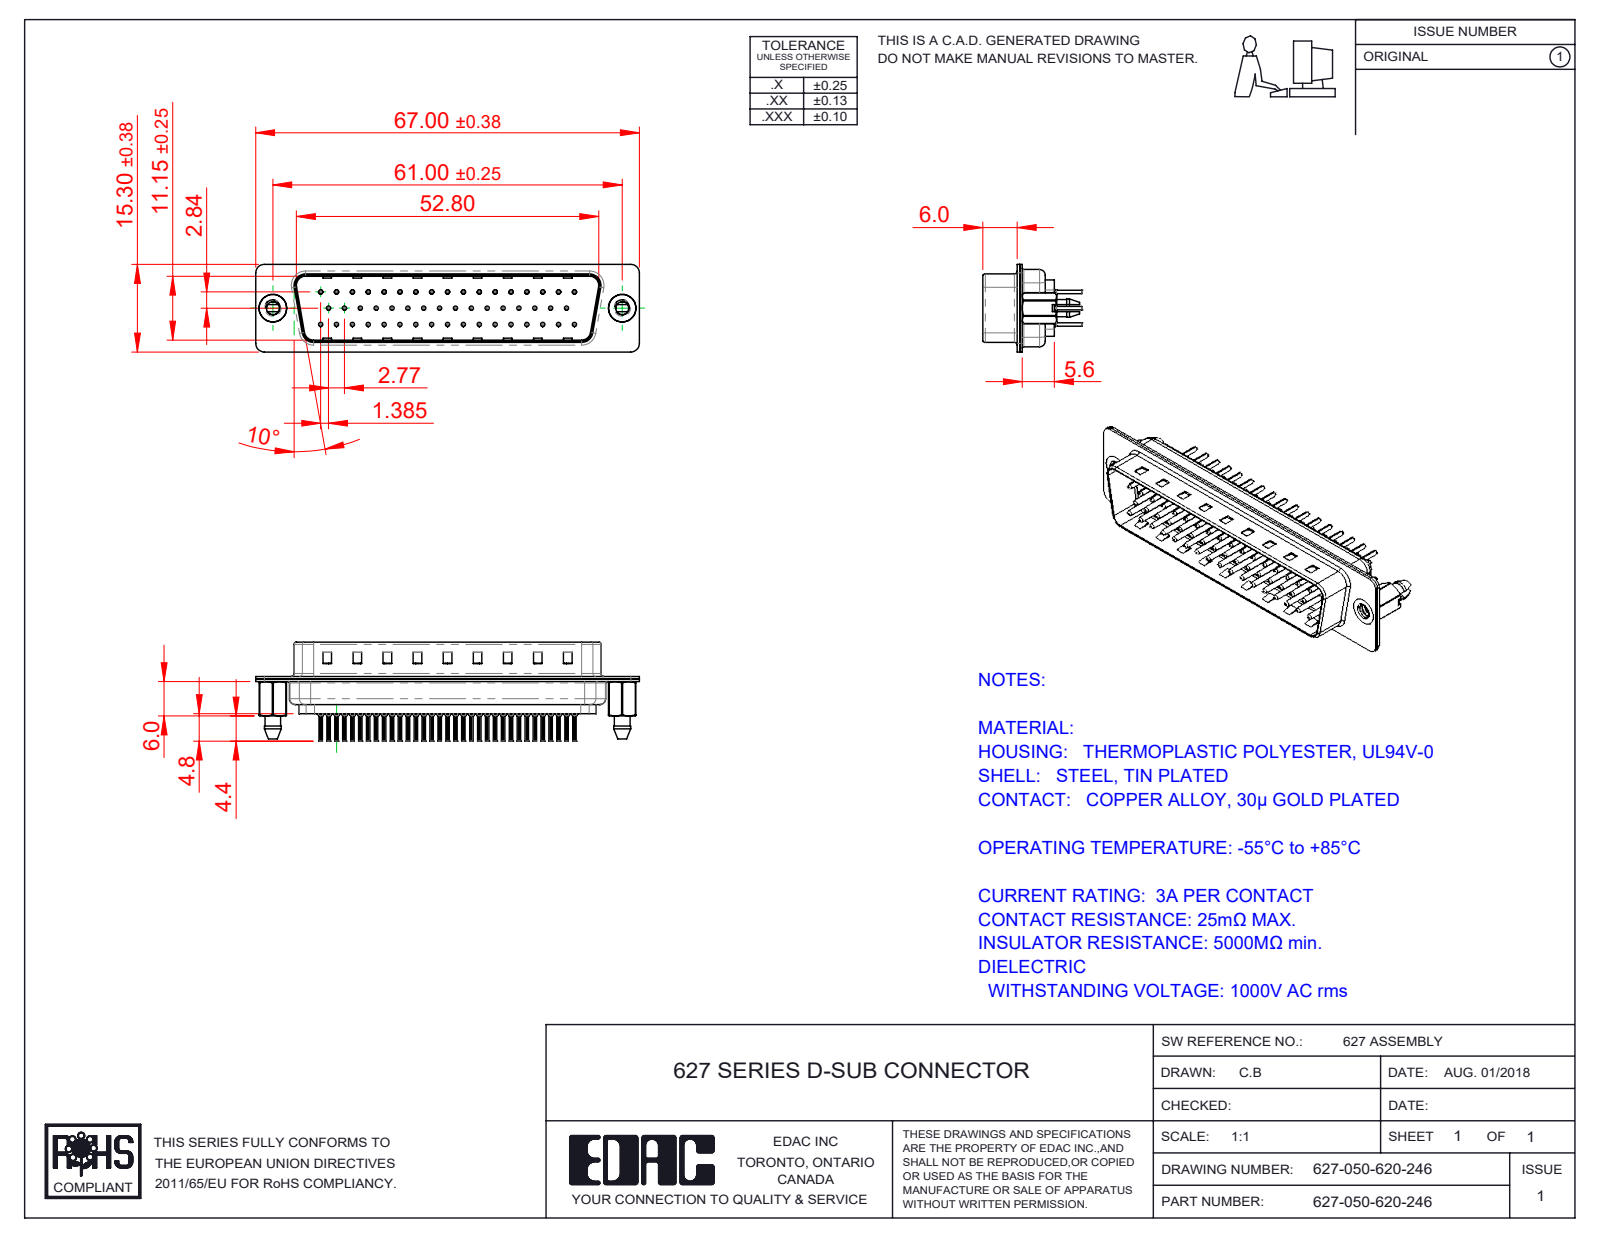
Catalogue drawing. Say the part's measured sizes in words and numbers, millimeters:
The part is named "627 Contact Row 2_20L; 627 Contact Row 1_20L; 627 4-40 Threaded Boardlock_LP; 627-050-620-046 (+4 more)". Its 3-D file was written by "SolidWorks 2020 (CONFIG_CONTROL_DESIGN)". It is 55 solids with 5386 faces: 1435 planar, 2023 cylindrical and 1928 other. Overall it measures 67 by 17.3 by 15.3 millimeters. Its volume is 4 539 cubic millimeters and its surface area 12 876 square millimeters. Round holes: 50 of diameter 0.2, 50 of diameter 0.35, 50 of diameter 1.1, 50 of diameter 1.6, 2 of diameter 2.26, 2 of diameter 4, 2 of diameter 4.8. Round bosses or shafts: 50 of diameter 2, 50 of diameter 1.5, 50 of diameter 0.75, 50 of diameter 0.6, 2 of diameter 4.9. Partial cylindrical surfaces (rounded edges, fillets, slot ends): 100 of radius 0.1, 18 of radius 1.5, 12 of radius 2, 10 of radius 1.6, 8 of radius 0.5, 4 of radius 0.25, 4 of radius 0.6, 4 of radius 0.65. The main face-to-face distances are 0.4, 0.45, 11.55, 6.05, 0.9, 6.5, 0.78, 12.33, 1.95, 0.77. The hole center spacings are 3.16, 2.77, 5.54, 8.31, 11.08, 13.85, 16.62, 5.03.
